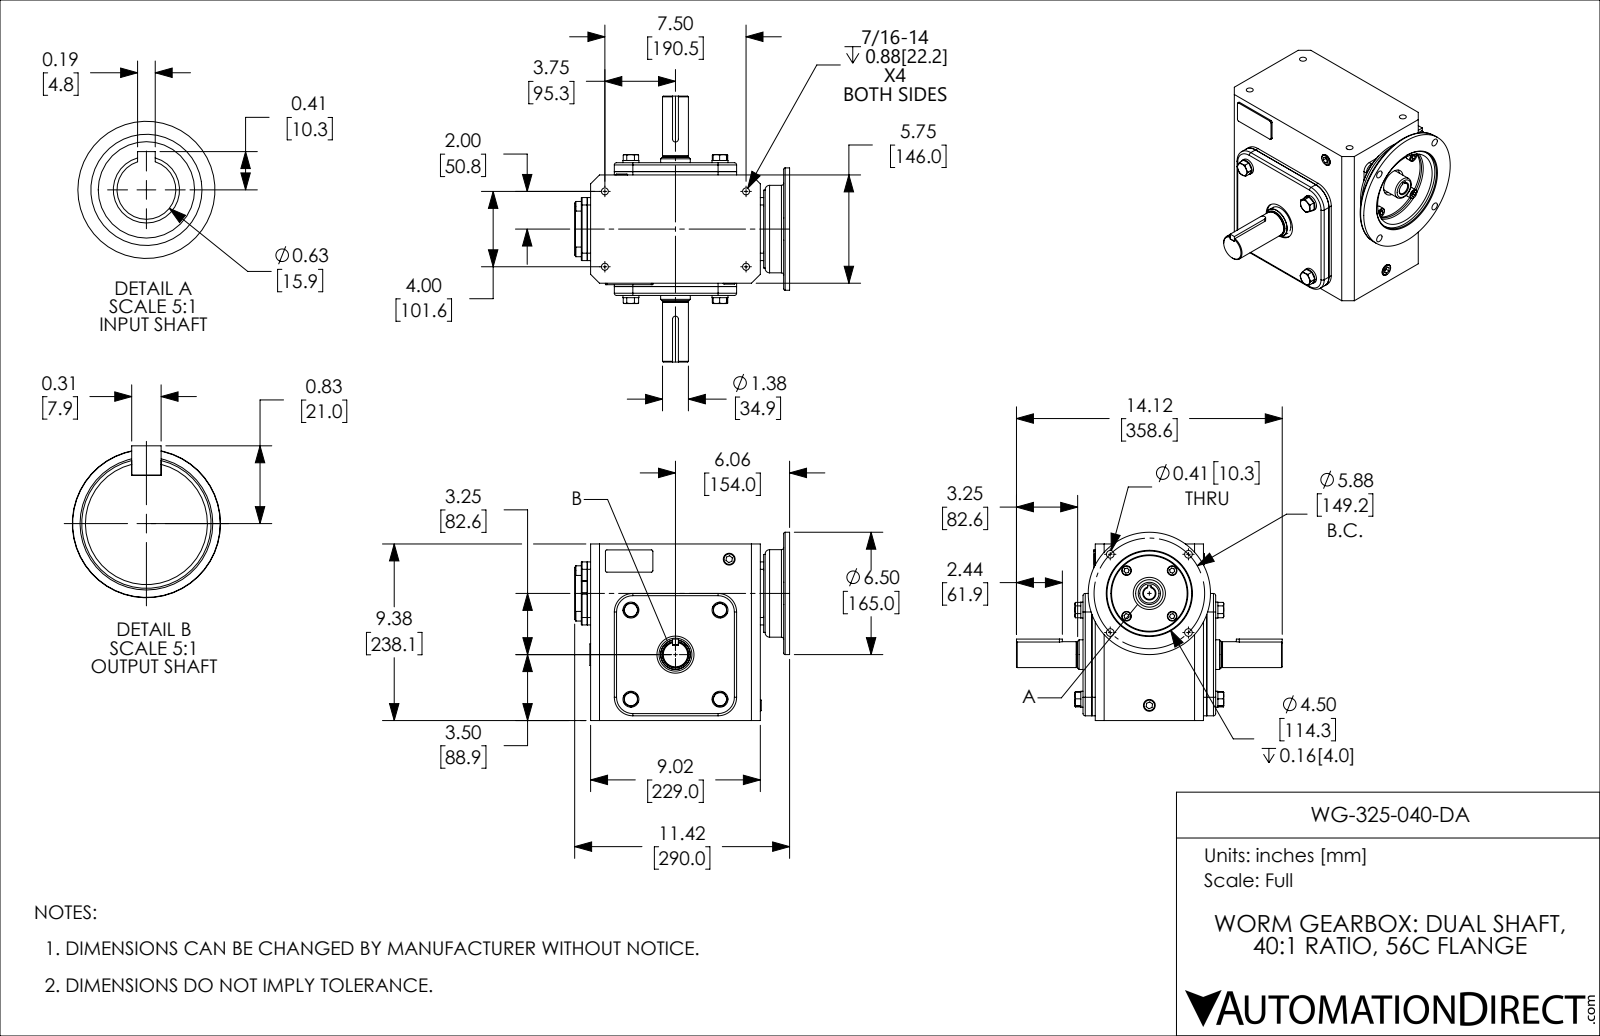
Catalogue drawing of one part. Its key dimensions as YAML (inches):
part_name: "WG-325-040-DA"
step_written_by: "SolidWorks 2017 (AUTOMOTIVE_DESIGN)"
units: inches
bodies: {solids: 42, faces: 612, planar: 331, cylindrical: 178, other: 103}
overall_size: [14.118, 11.417, 9.998]
volume: 515.7
surface_area: 936.5
round_holes:
  - {diameter: 0.368, count: 4}
  - {diameter: 0.406, count: 4}
  - {diameter: 0.628, count: 3}
  - {diameter: 0.591, count: 1}
  - {diameter: 0.625, count: 1}
  - {diameter: 0.978, count: 1}
  - {diameter: 1.181, count: 1}
  - {diameter: 1.457, count: 1}
  - {diameter: 1.969, count: 1}
  - {diameter: 2.441, count: 1}
  - {diameter: 2.756, count: 1}
  - {diameter: 4.016, count: 1}
round_bosses_or_shafts:
  - {diameter: 0.846, count: 4}
  - {diameter: 0.512, count: 4}
  - {diameter: 6.496, count: 1}
  - {diameter: 4.646, count: 1}
  - {diameter: 4.134, count: 1}
  - {diameter: 2.835, count: 1}
  - {diameter: 1.575, count: 1}
  - {diameter: 1.375, count: 1}
partial_cylinders:
  - {radius: 0.118, count: 8}
  - {radius: 0.079, count: 7}
  - {radius: 0.394, count: 4}
  - {radius: 0.906, count: 4}
  - {radius: 0.984, count: 4}
  - {radius: 0.02, count: 2}
  - {radius: 0.039, count: 2}
  - {radius: 0.156, count: 2}
face_to_face_distances: [0.079, 0.177, 6.496, 0.394, 6.969, 0.472, 6.575, 6.398, 0.571, 0.65]
hole_center_spacings: [2.937, 4.154, 2.385, 4, 4.389, 5.718, 5.817, 5.875]
